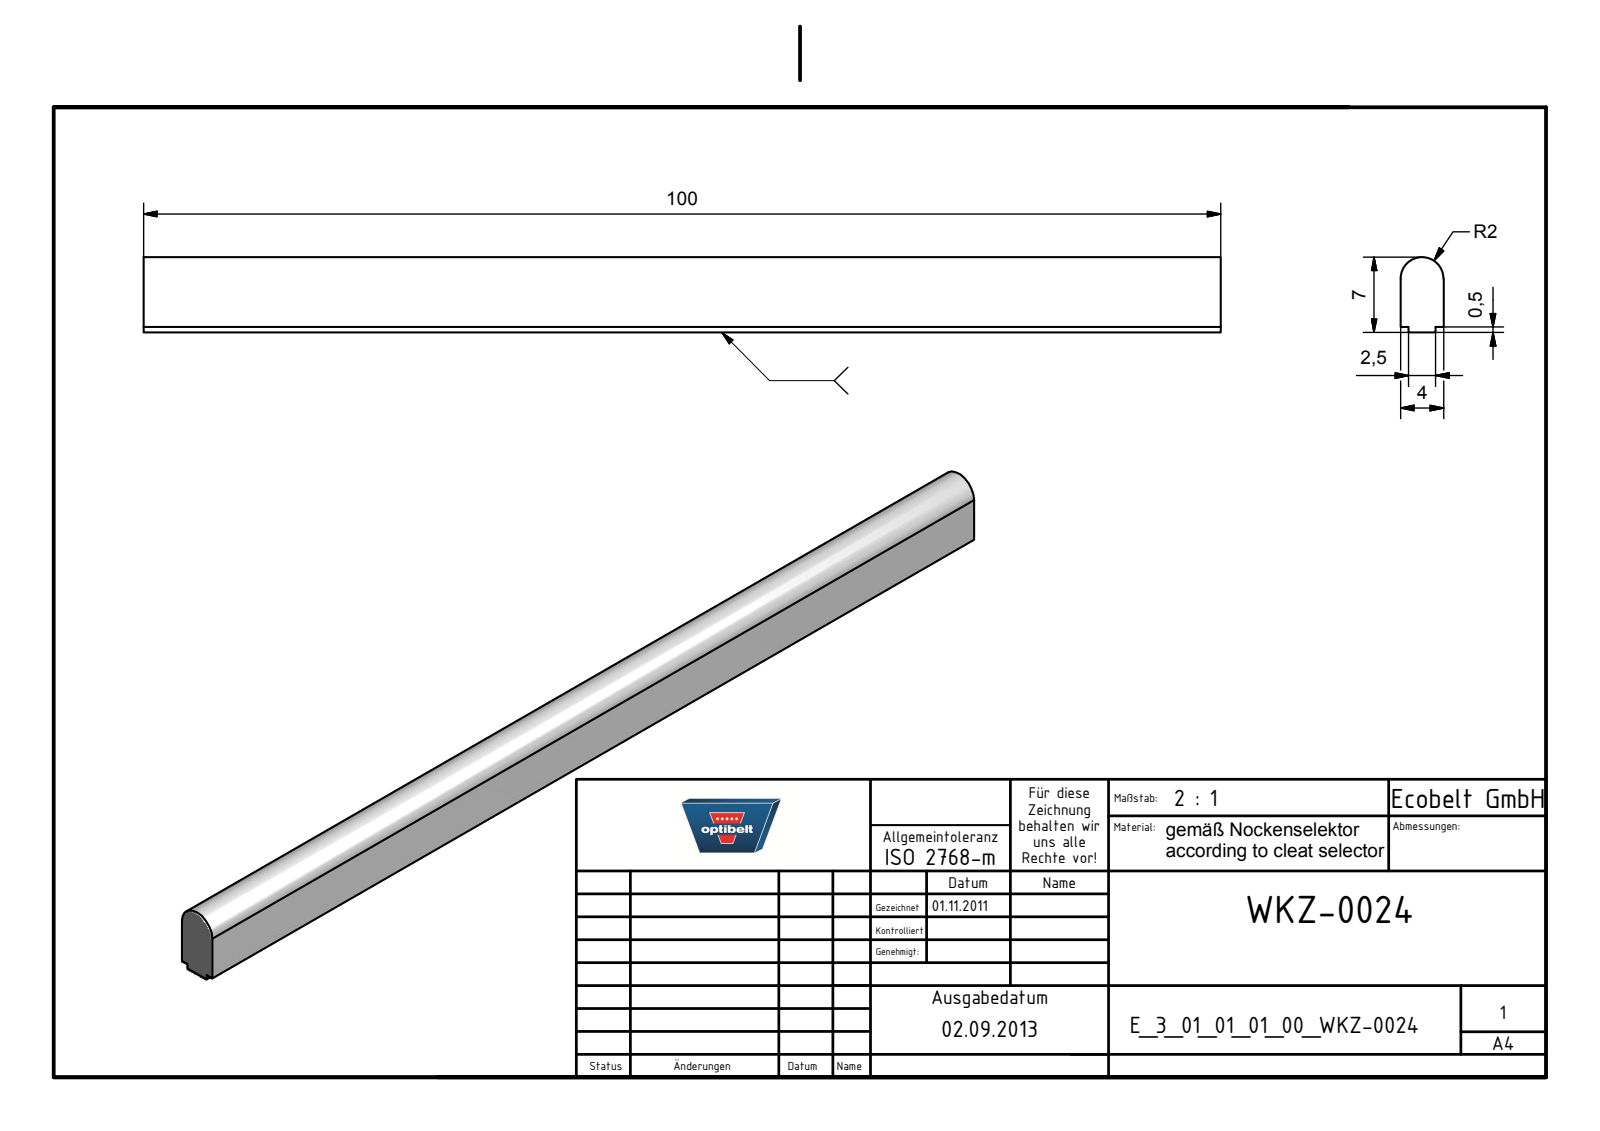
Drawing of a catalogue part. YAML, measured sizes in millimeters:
part_name: "E_3_01_01_01_00_WKZ-0024"
step_written_by: "Autodesk Inventor 2021 (AUTOMOTIVE_DESIGN)"
units: millimeters
bodies: {solids: 1, faces: 10, planar: 9, cylindrical: 1, other: 0}
overall_size: [100, 7, 4]
volume: 2553
surface_area: 2079
partial_cylinders:
  - {radius: 2, count: 1}
face_to_face_distances: [4, 0.5, 0.75, 3.25, 2.5, 100]
